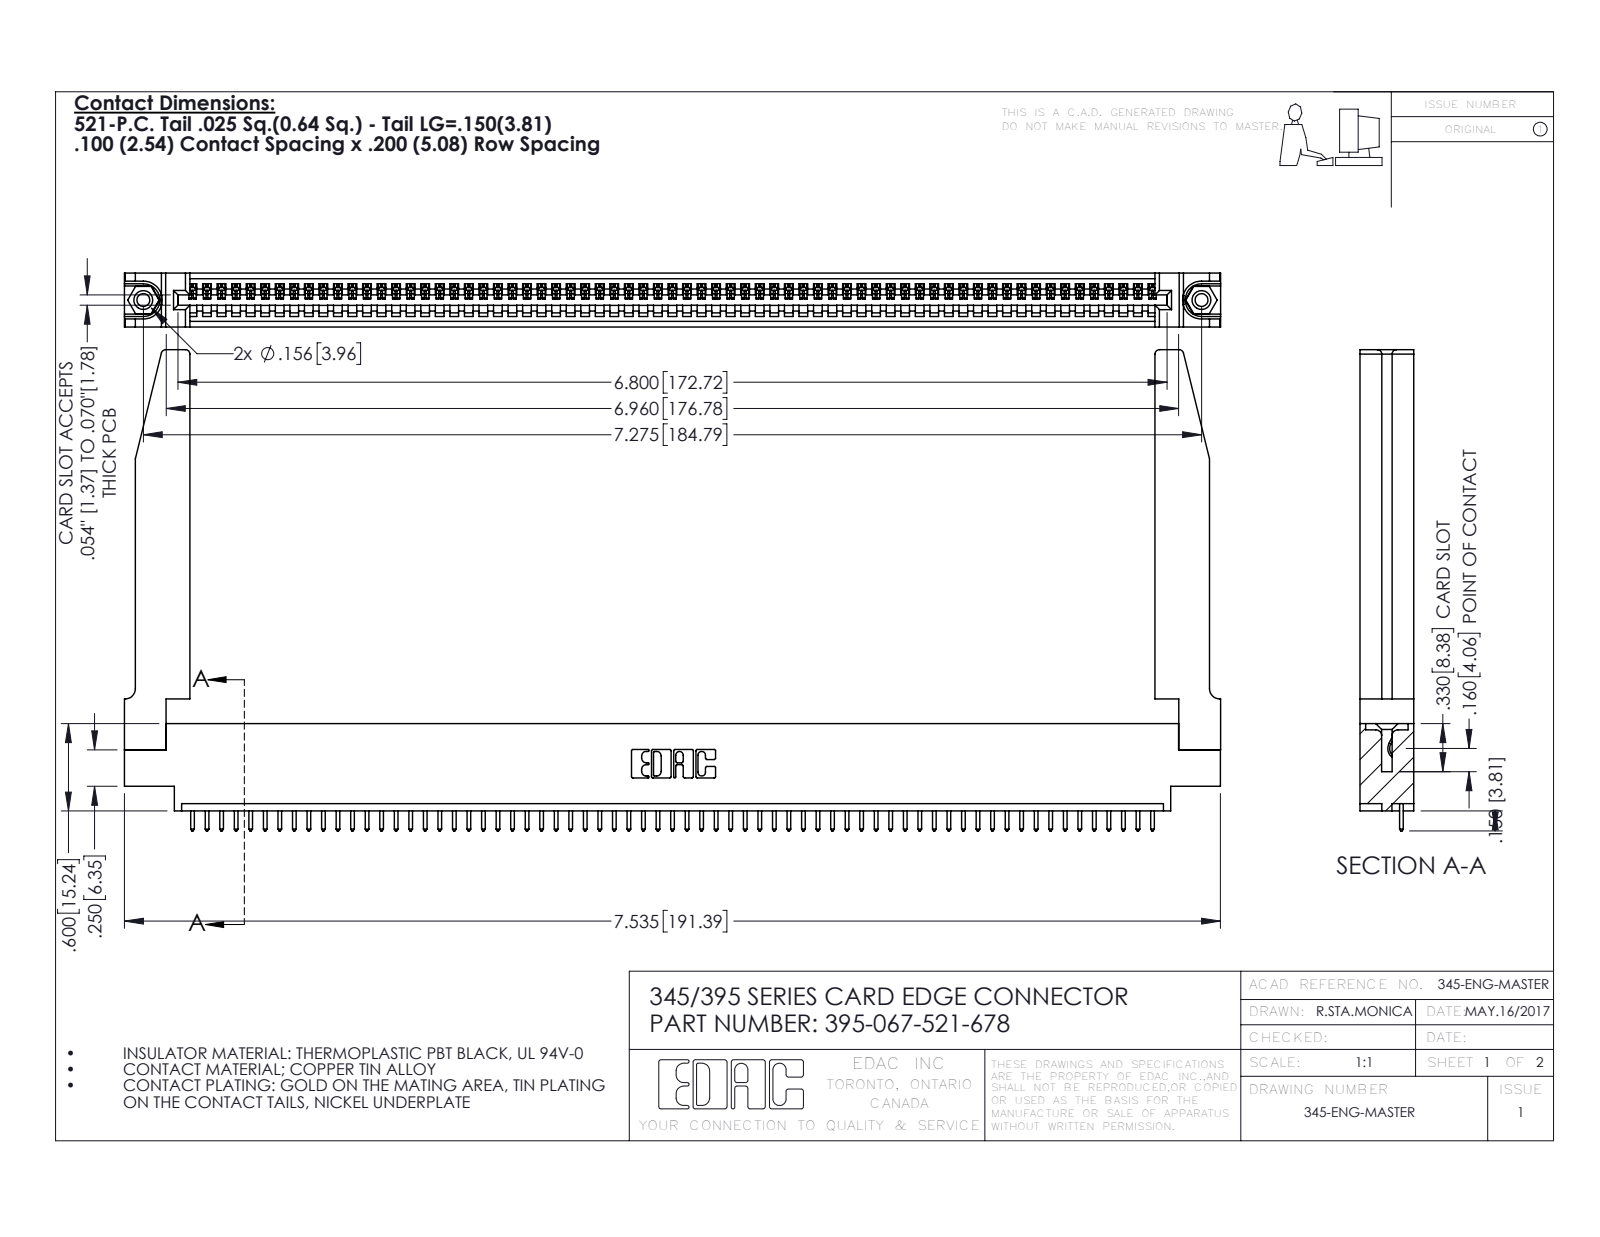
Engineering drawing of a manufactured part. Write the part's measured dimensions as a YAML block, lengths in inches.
part_name: "345-220-078_345-220-078; 345-250-001_345-250-001-102; 395-067-521-678; 345 Part_0.170 Offset - 0.156 Dia-TH (+1 more)"
step_written_by: "SolidWorks 2016 (CONFIG_CONTROL_DESIGN)"
units: inches
bodies: {solids: 72, faces: 4250, planar: 2906, cylindrical: 1292, other: 52}
overall_size: [7.536, 3.307, 0.37]
volume: 1.578
surface_area: 47.42
round_holes:
  - {diameter: 0.089, count: 2}
  - {diameter: 0.125, count: 2}
  - {diameter: 0.156, count: 2}
  - {diameter: 0.064, count: 1}
round_bosses_or_shafts:
  - {diameter: 0.155, count: 2}
partial_cylinders:
  - {radius: 0.006, count: 134}
  - {radius: 0.01, count: 134}
  - {radius: 0.01, count: 22}
  - {radius: 0.03, count: 8}
  - {radius: 0.007, count: 6}
  - {radius: 0.031, count: 6}
  - {radius: 0.026, count: 3}
  - {radius: 0.031, count: 2}
face_to_face_distances: [0.37, 0.072, 0.298, 0.098, 0.272, 0.025, 0.2, 0.225, 0.175, 0.149]
hole_center_spacings: [0.27, 7.039, 7.275]
